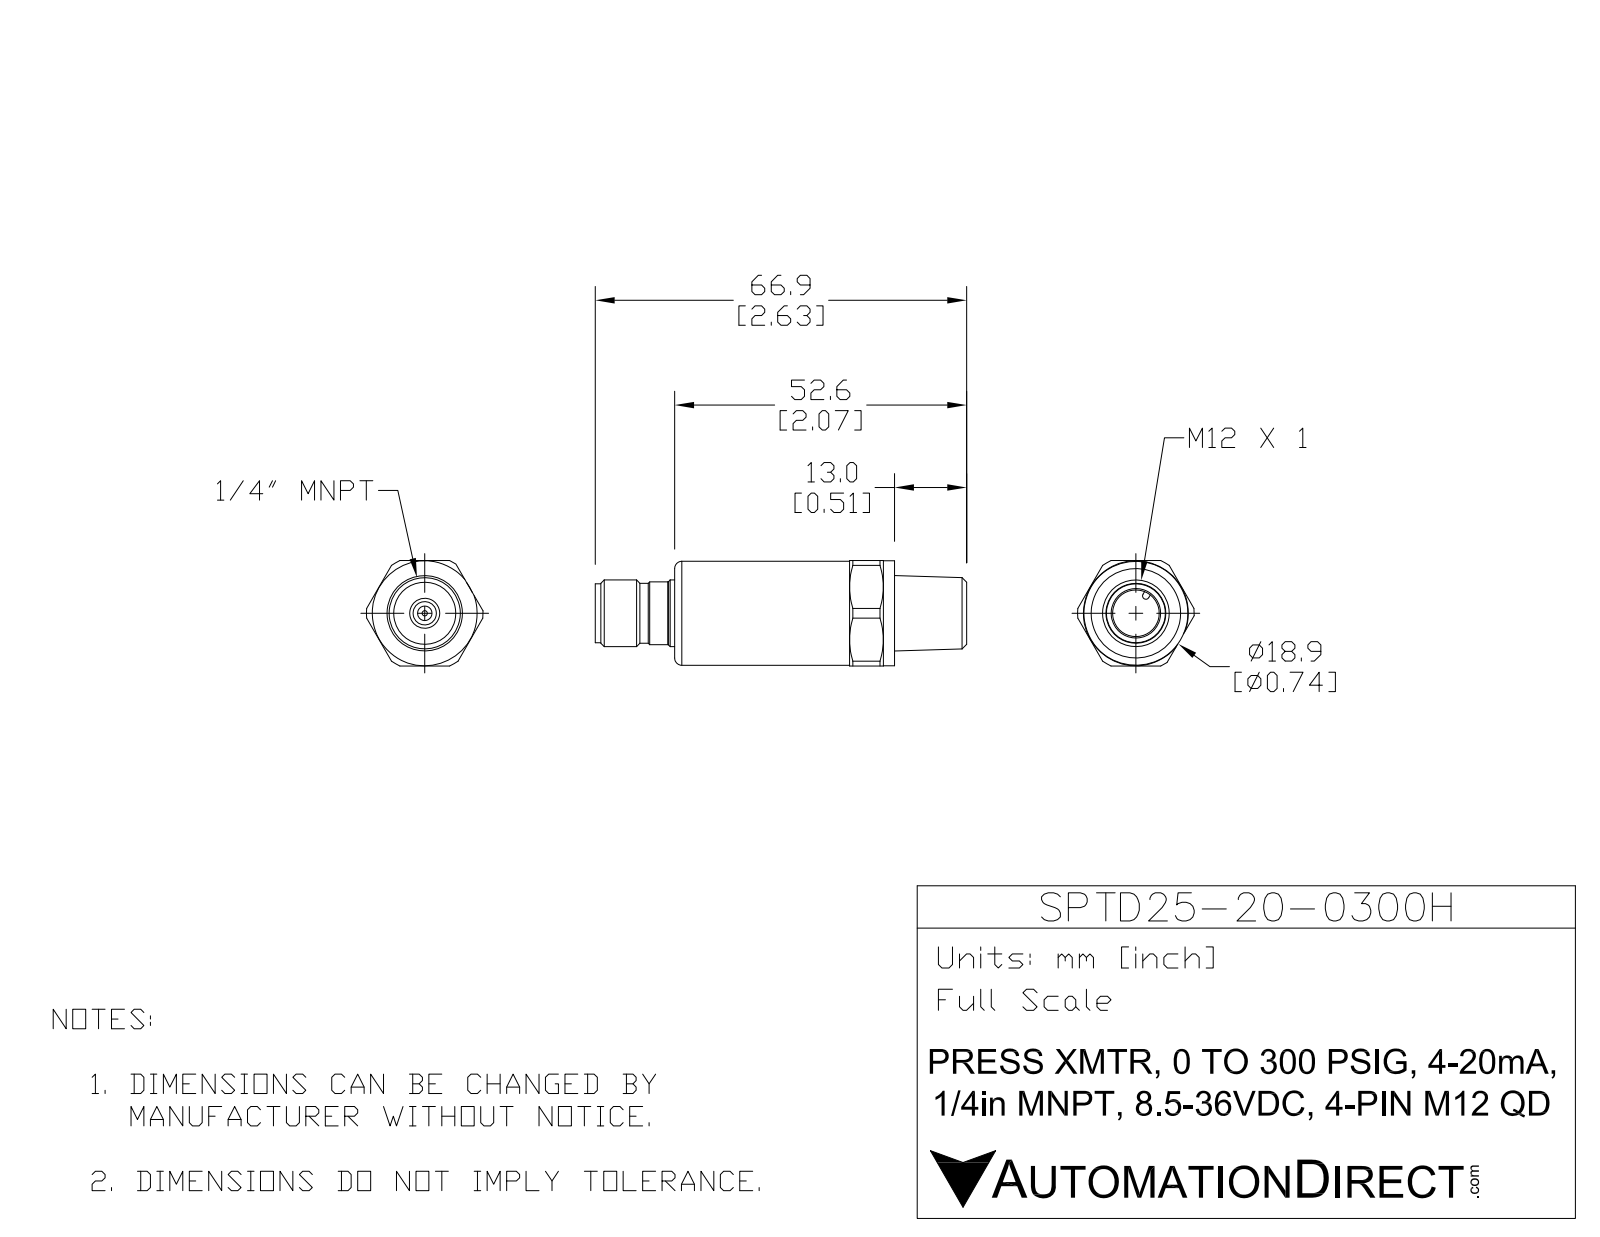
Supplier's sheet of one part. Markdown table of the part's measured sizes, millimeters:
| quantity | value |
| --- | --- |
| part name | SPDT25-20-0300H |
| STEP written by | SolidWorks 2015 (AUTOMOTIVE_DESIGN) |
| units | millimeters |
| bodies | 7 solids, 177 faces (44 planar, 53 cylindrical, 80 other) |
| overall size | 66.9 × 21.57 × 18.9 |
| volume | 13 446 mm³ |
| surface area | 5 337 mm² |
| round holes (diameter × count) | 4.2 × 1, 8.4 × 1, 16.6 × 1 |
| round bosses / shafts (diameter × count) | 1.4 × 4, 1 × 4, 18.9 × 1, 12 × 1, 11.3 × 1, 10.8 × 1, 10.6 × 1, 10.5 × 1 |
| partial cylindrical surfaces (radius × count) | 0.61 × 1 |
| main face-to-face distances | 18.9, 52.55, 13.09, 39.46, 58.1, 45.01, 5.55, 14.29, 1.2, 38.26 |
